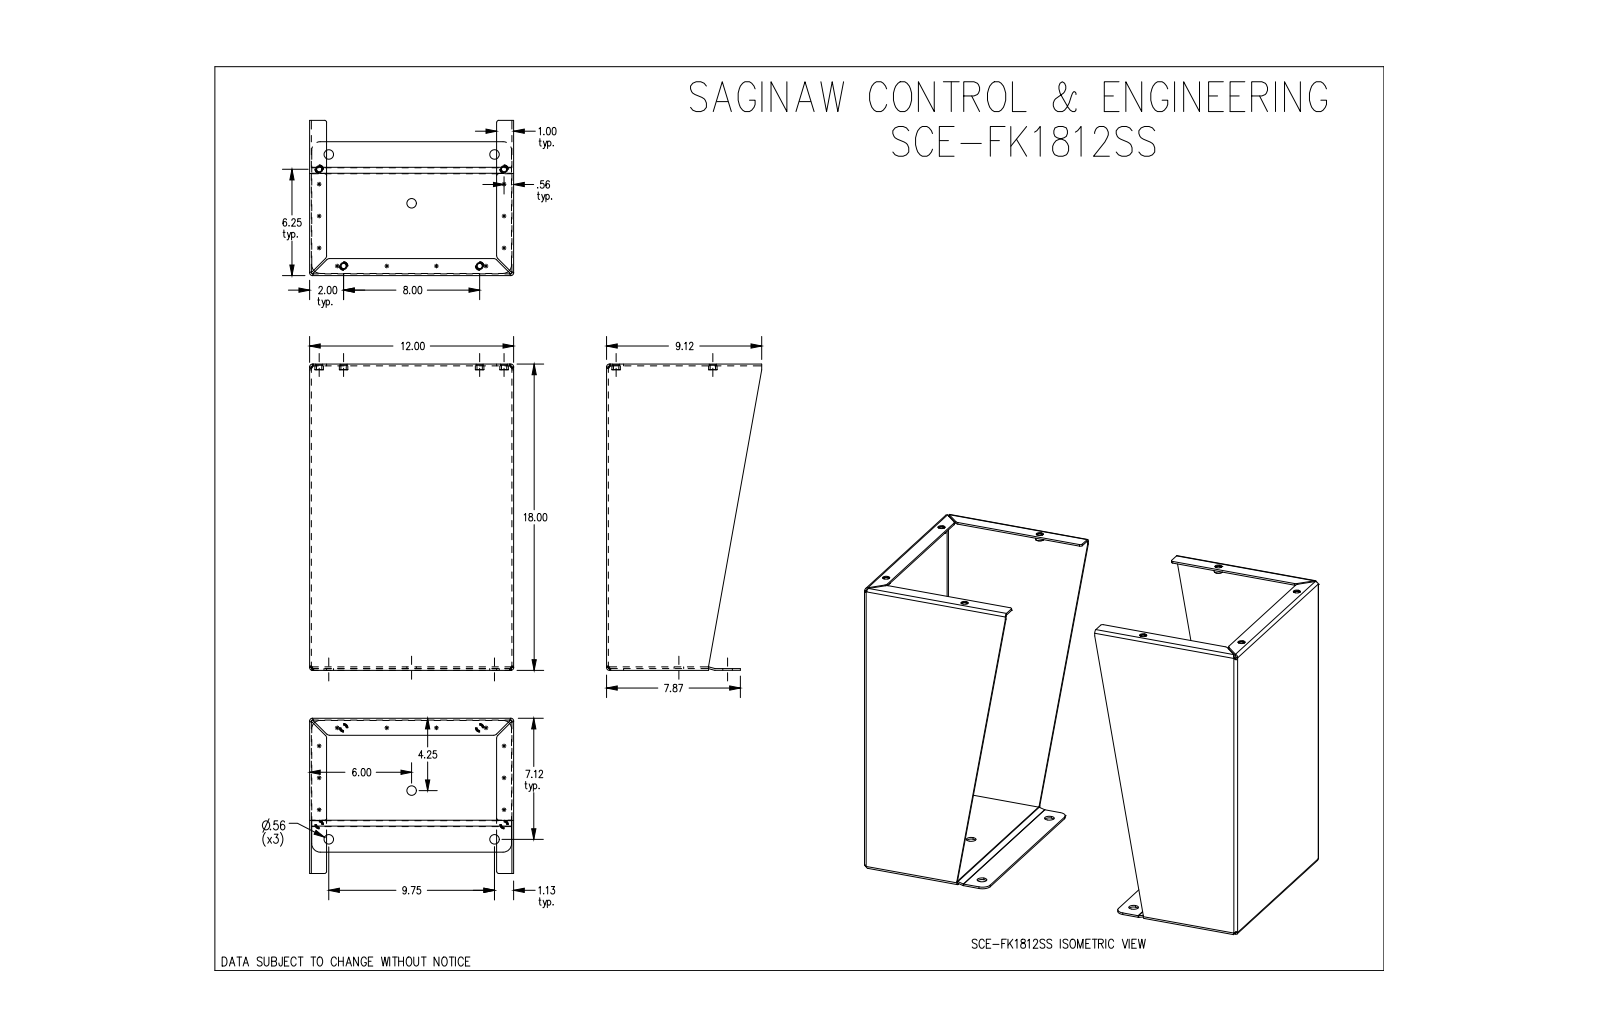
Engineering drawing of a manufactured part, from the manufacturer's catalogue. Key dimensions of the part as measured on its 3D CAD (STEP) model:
Part name (STEP PRODUCT): SCE-FK1812SS
STEP written by: SolidWorks 2019 (CONFIG_CONTROL_DESIGN)
Units: inches
Bodies: 12 solids, 286 faces (120 planar, 110 cylindrical, 56 other)
Overall size (bounding box): 24 × 18 × 12
Volume: 127.9 in³ · Surface area: 2 493 in²
Round holes (diameter × count): ⌀0.312 ×8, ⌀0.413 ×8, ⌀0.563 ×6
Round bosses / shafts (diameter × count): ⌀0.5 ×8, ⌀0.412 ×8
Partial cylindrical surfaces — rounded edges, fillets, slot ends (radius × count): R0.166 ×16, R0.062 ×12, R0.125 ×8, R0.22 ×8, R0.5 ×8, R0.063 ×6
Main face-to-face distances: 0.104, 11.896, 23.896, 12, 11.792, 23.792, 24, 17.792, 17.896, 0.101
Hole centre spacings: 1.035, 5.441, 5.656, 5.793, 5.866, 6.614, 10.646, 11.019
